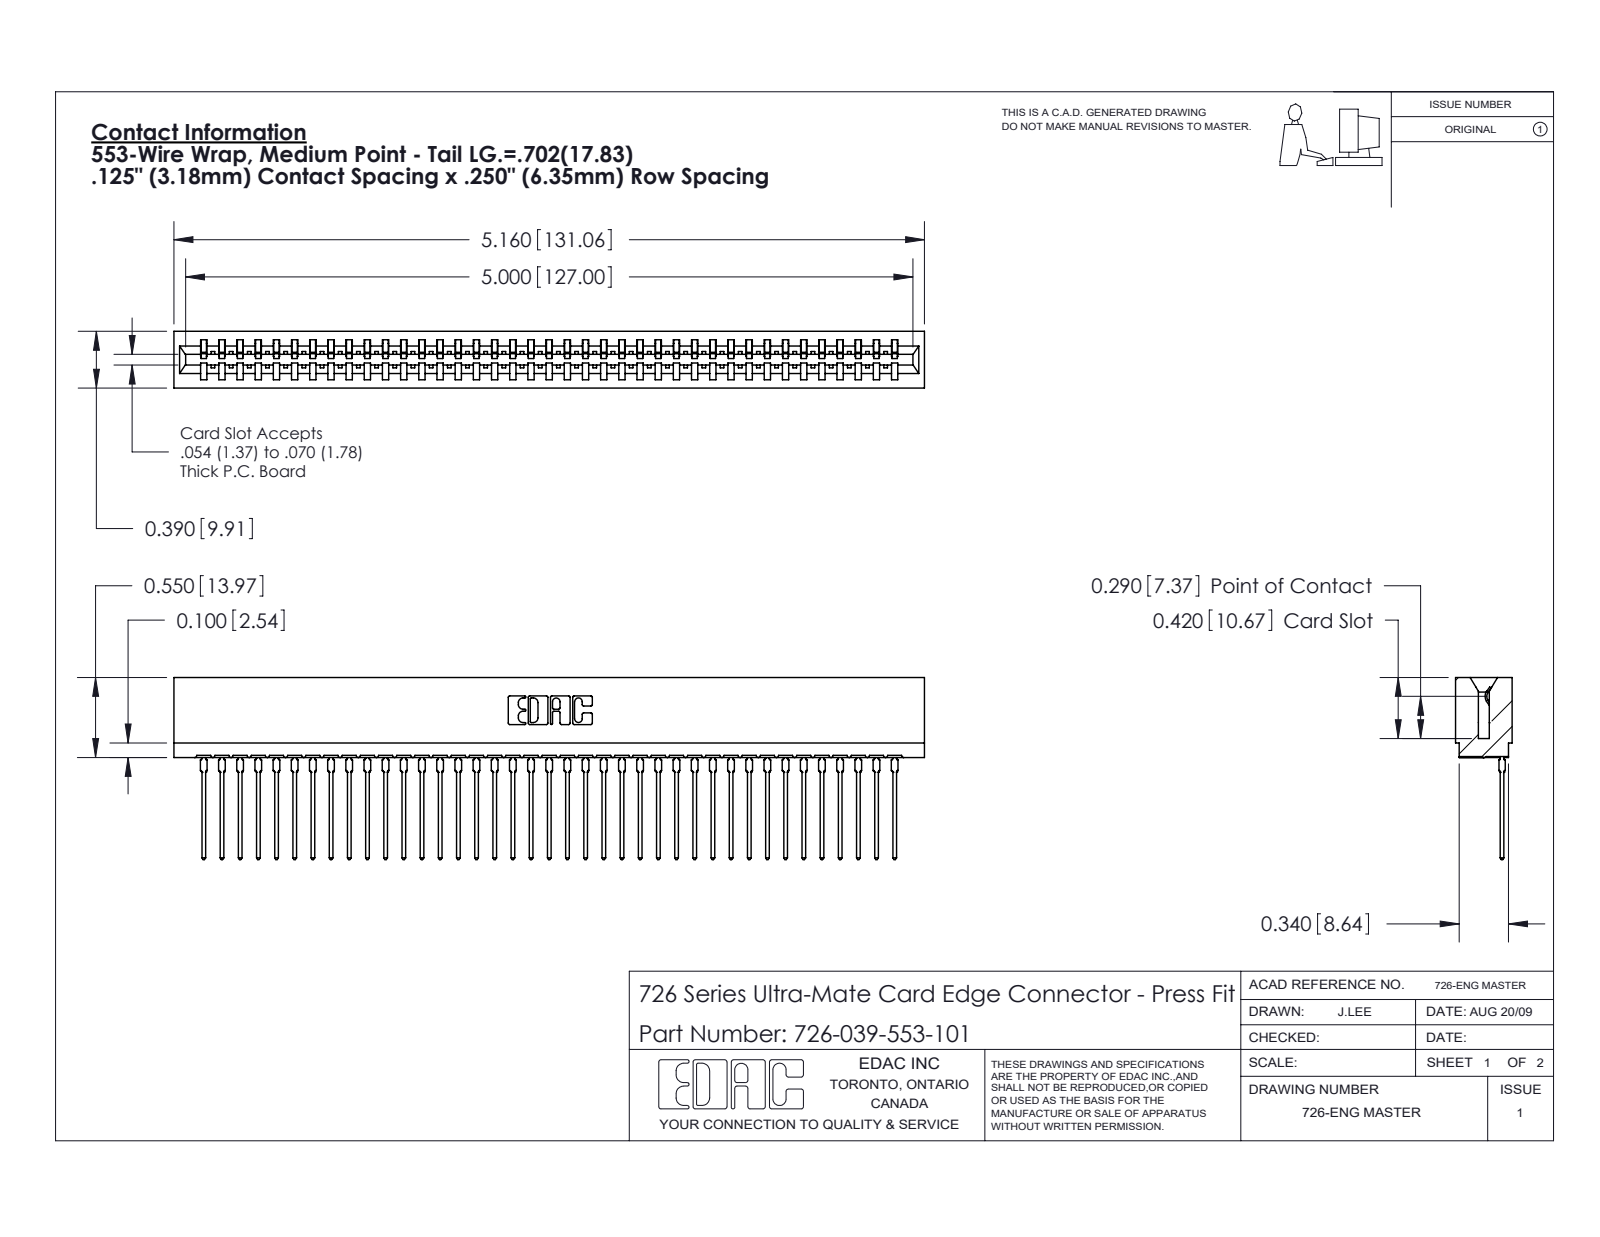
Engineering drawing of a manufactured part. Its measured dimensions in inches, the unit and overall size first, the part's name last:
Units: inches
Overall size (bounding box): 5.16 × 1.251 × 0.39
Partial cylindrical surfaces — rounded edges, fillets, slot ends (radius × count): R0.021 ×78, R0.015 ×40, R0.01 ×22, R0.007 ×6, R0.031 ×6, R0.005 ×4, R0.011 ×4, R0.026 ×3
Main face-to-face distances: 0.057, 0.333, 0.39, 0.025, 0.307, 0.25, 0.083, 0.275, 0.365, 0.032
Volume: 0.724 in³ · Surface area: 29.12 in²
Bodies: 40 solids, 4309 faces (2512 planar, 783 cylindrical, 1014 other)
Part name (STEP PRODUCT): 726 Part_.515 Slot Depth - 01; 746-292-001_553; 726-039-553-101
STEP written by: SolidWorks 2020 (CONFIG_CONTROL_DESIGN)
